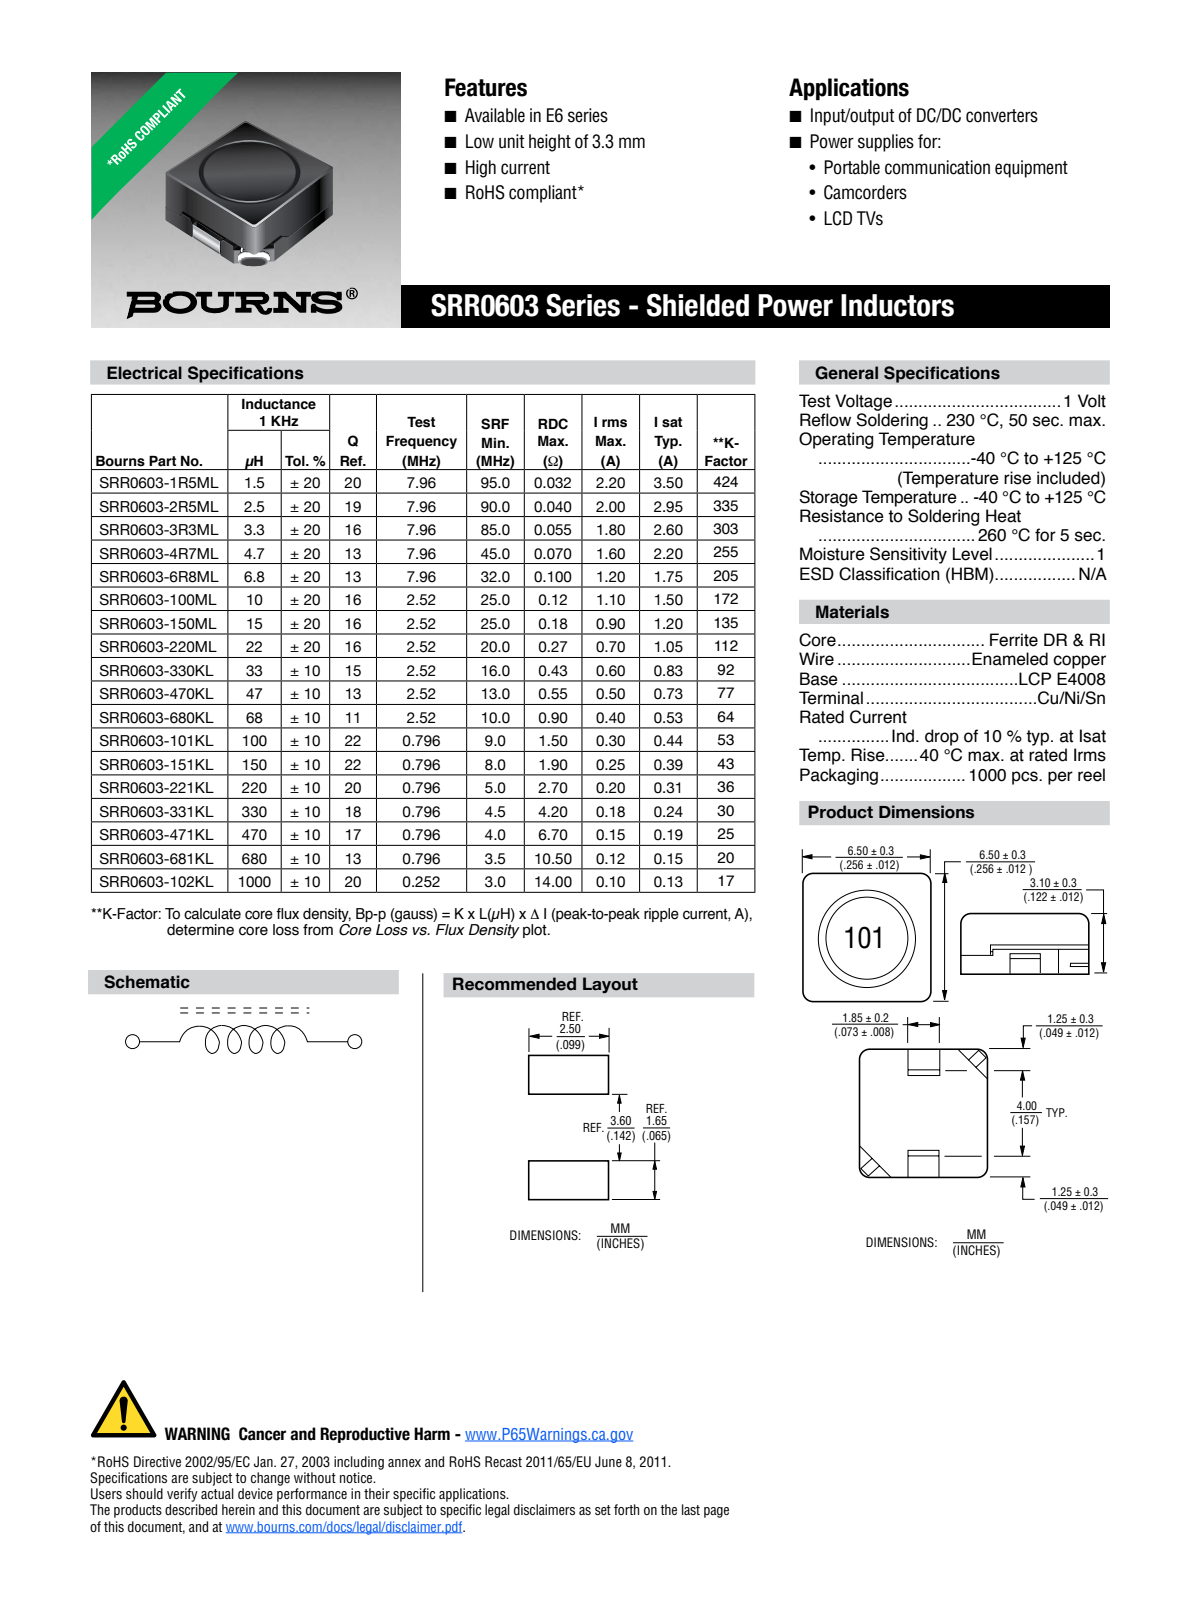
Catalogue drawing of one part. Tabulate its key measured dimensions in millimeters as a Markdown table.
| quantity | value |
| --- | --- |
| part name | SS0603 |
| STEP written by | ZW3D to STEP translator (CONFIG_CONTROL_DESIGN) |
| units | millimeters |
| bodies | 10 solids, 241 faces (0 planar, 0 cylindrical, 241 other) |
| overall size | 6.5 × 6.5 × 3.13 |
| volume | 95 mm³ |
| surface area | 383 mm² |
